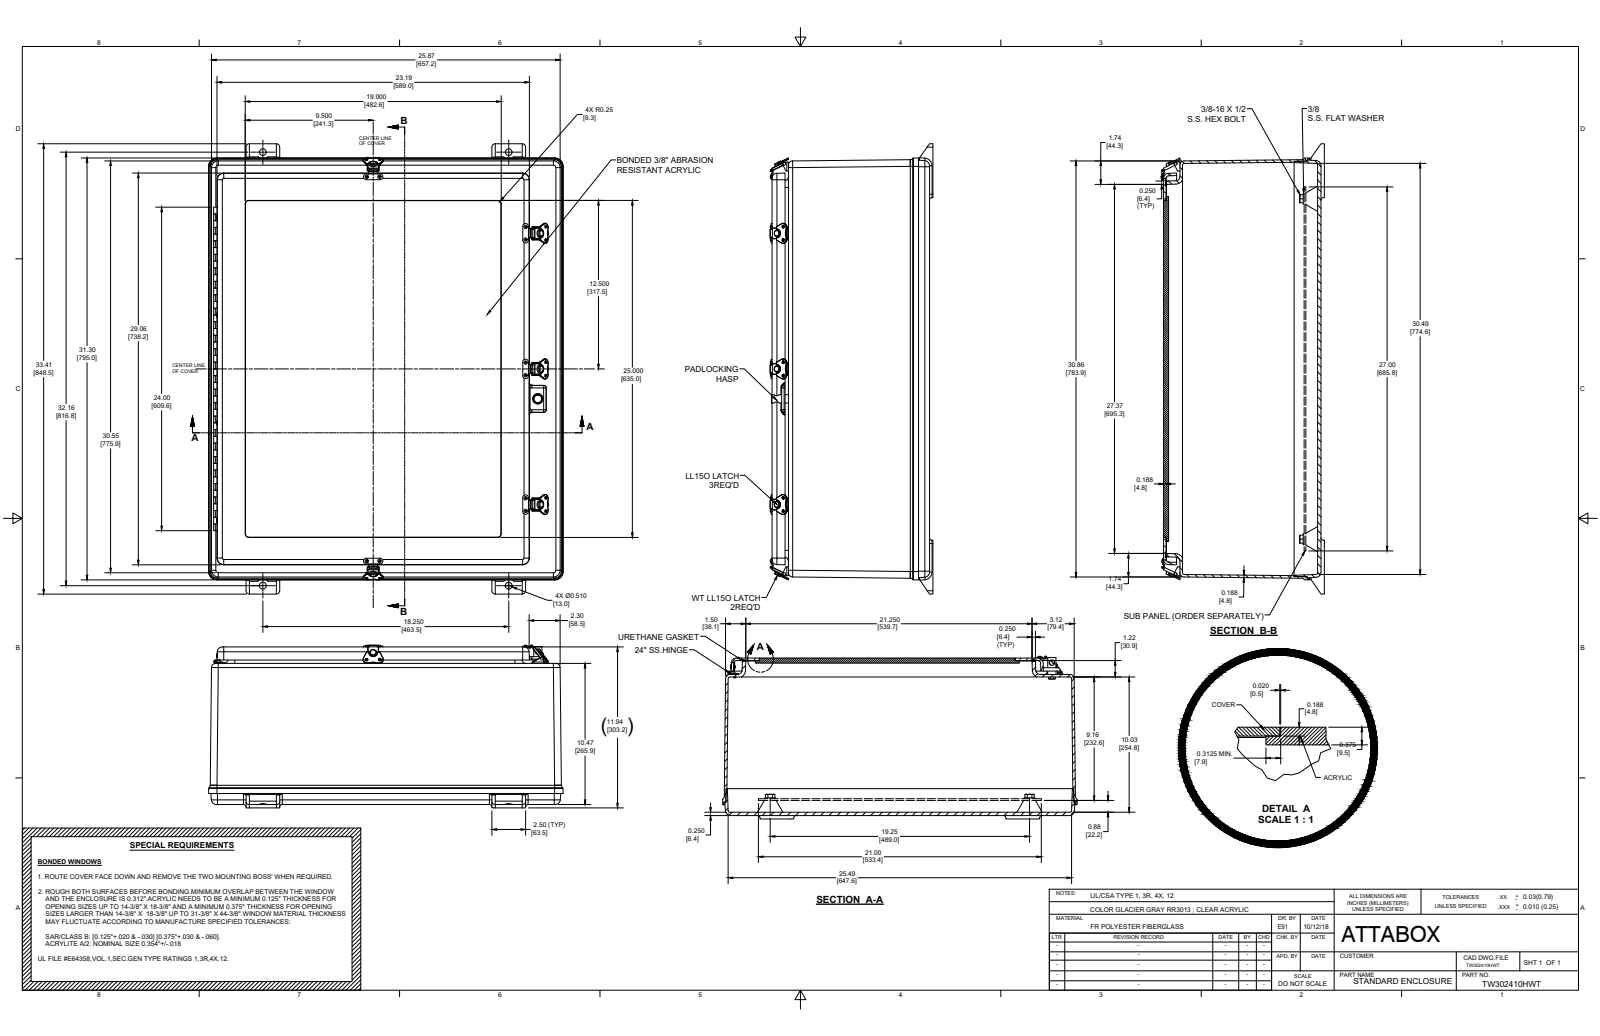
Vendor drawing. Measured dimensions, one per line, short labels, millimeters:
name: TW302410HWT
written by: SolidWorks 2018 (AUTOMOTIVE_DESIGN)
unit: mm
bodies: 68 solids, 1862 faces (702 planar, 722 cylindrical, 438 other)
size: 848.5 × 668.4 × 307
volume: 12 100 000 mm³; area: 4 309 000 mm²
holes: 36× ⌀3.3, 20× ⌀1.6, 10× ⌀3.5, 10× ⌀4.7, 5× ⌀1.7, 4× ⌀7.8, 4× ⌀14.3, 3× ⌀1.7, 3× ⌀3.4, 3× ⌀4, 2× ⌀12.7, 2× ⌀13
bosses: 20× ⌀3.6, 8× ⌀7.5, 5× ⌀12.7, 3× ⌀5.1, 1× ⌀6.4, 1× ⌀5.1, 1× ⌀3.4
rounds: 127× R0.3, 28× R6.4, 20× R0.8, 19× R4.7, 18× R7.9, 13× R9.5, 12× R12.7, 10× R3.2
face distances: 4.7, 6.4, 297, 290.6, 287.5, 281.1, 9.5, 4.8, 31.1, 292.2
hole spacings: 255.4, 184.2, 387.4, 25.4, 88.6, 256.2, 510.9, 729.2
